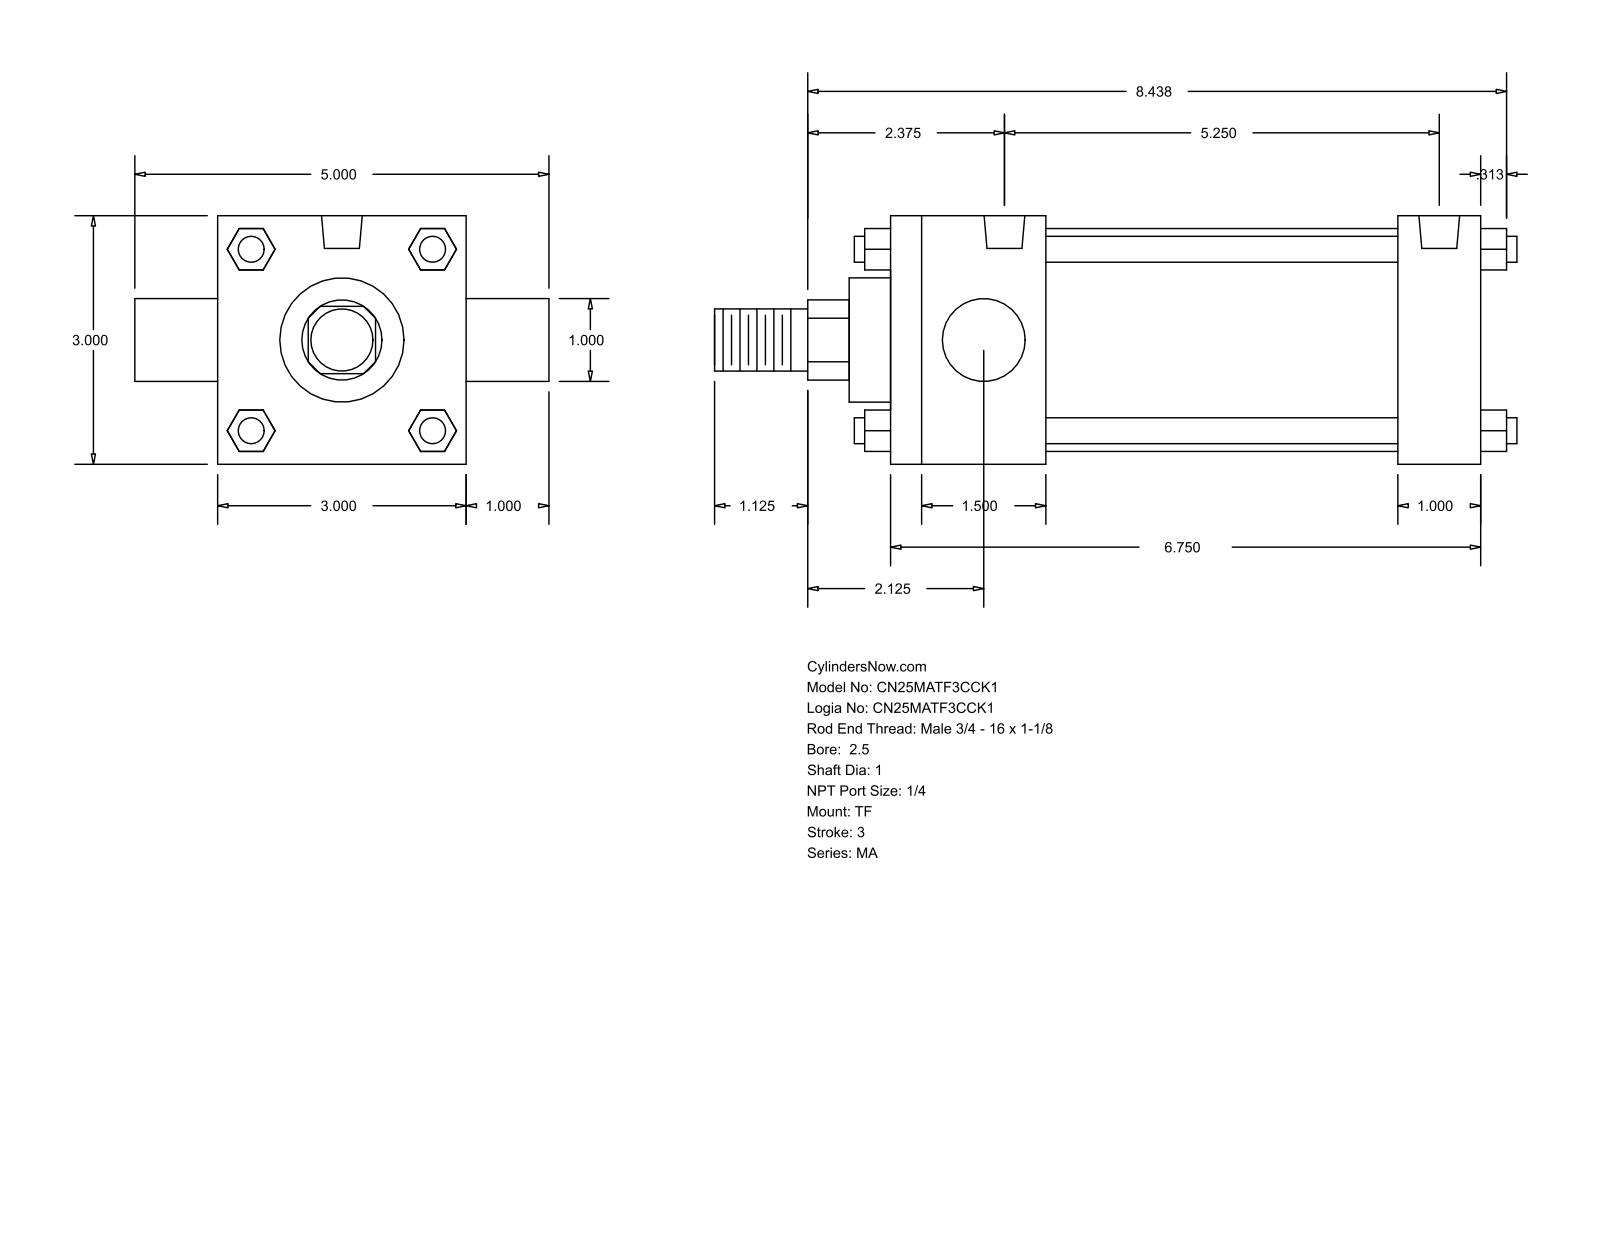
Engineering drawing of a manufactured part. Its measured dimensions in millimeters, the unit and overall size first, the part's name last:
Units: millimetres
Overall size (bounding box): 246.06 × 127 × 76.2
Round holes (diameter × count): ⌀7.94 ×3, ⌀12.49 ×2
Round bosses / shafts (diameter × count): ⌀7.94 ×4, ⌀25.4 ×2, ⌀68.33 ×1, ⌀38.1 ×1, ⌀19.05 ×1
Partial cylindrical surfaces — rounded edges, fillets, slot ends (radius × count): R12.29 ×1
Main face-to-face distances: 76.2, 180.98, 12.7, 47.63, 155.57, 107.94, 133.35, 25.41, 101.6, 25.4
Hole centre spacings: 133.35
Bodies: 0 solids, 120 faces (92 planar, 28 cylindrical, 0 other)
Part name (STEP PRODUCT): MA_TF__0250_1
STEP written by: GSSL Pune (CONFIG_CONTROL_DESIGN)
